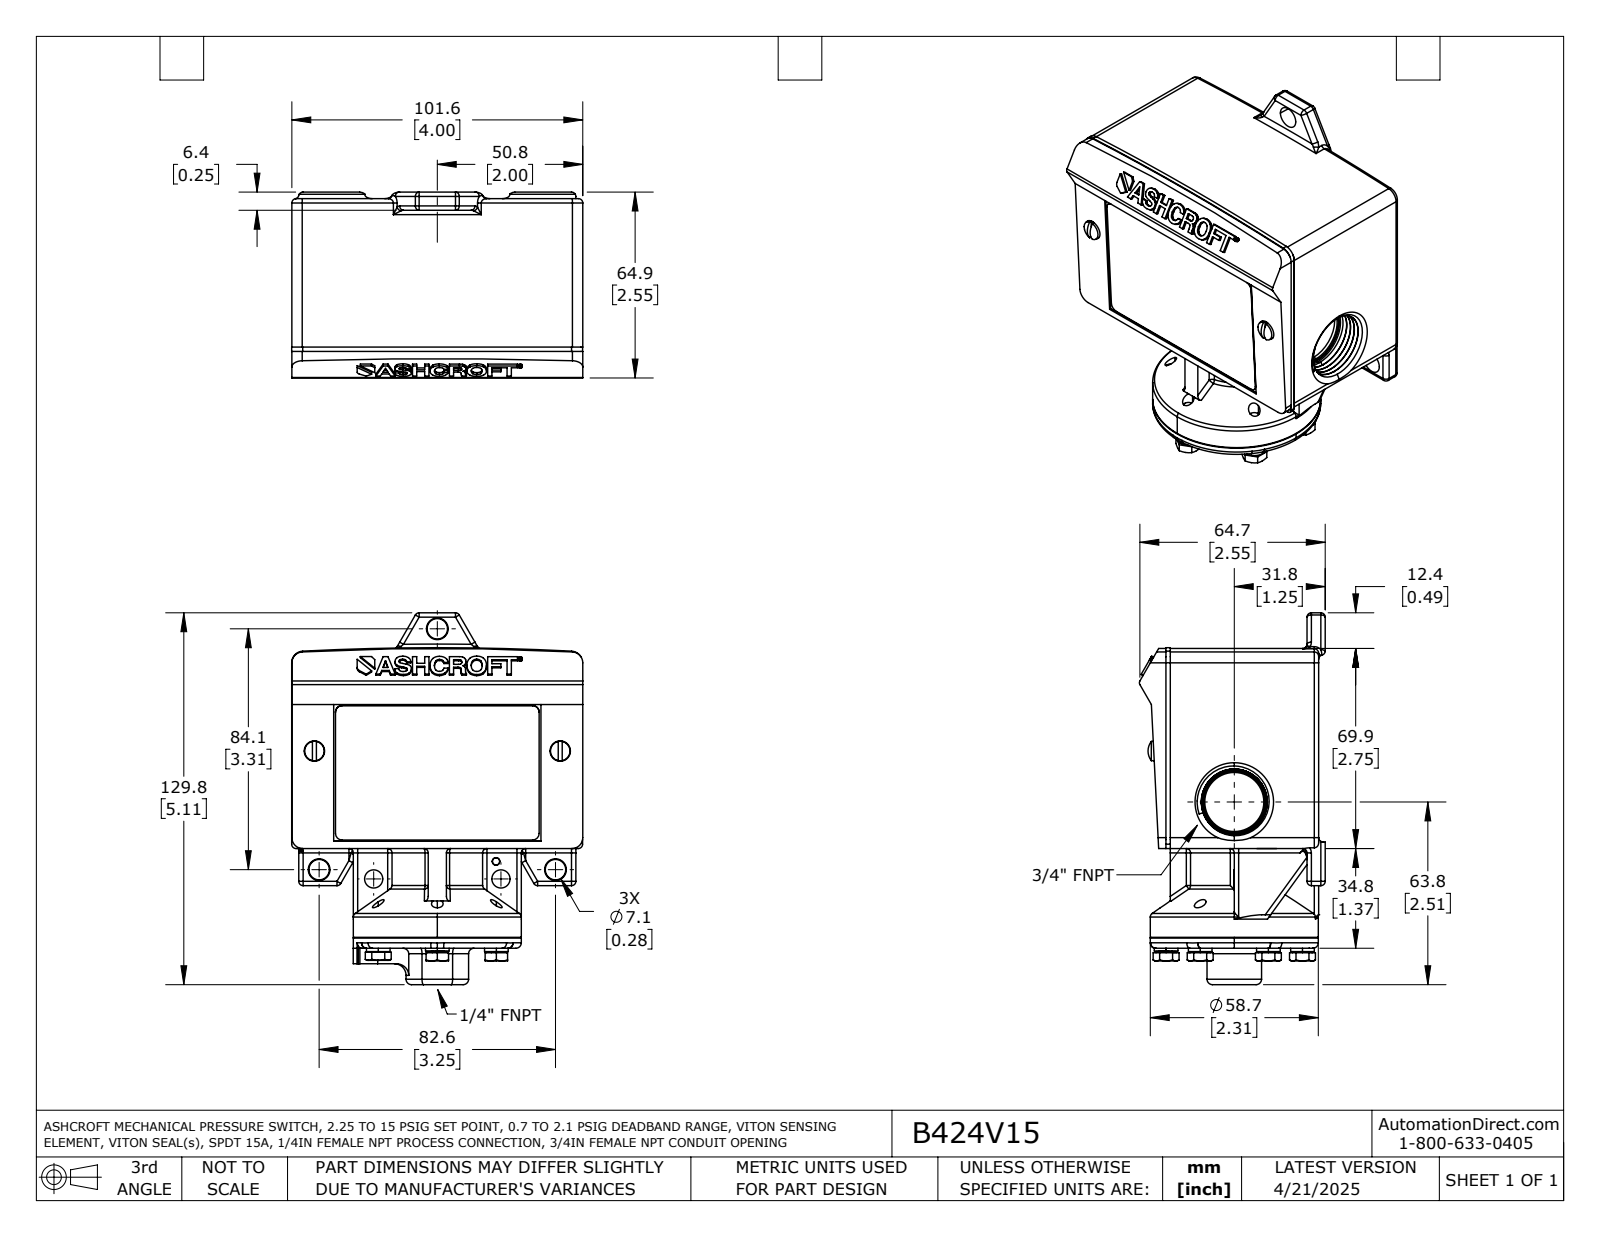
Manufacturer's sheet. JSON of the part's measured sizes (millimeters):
{"part_name": "B424V15", "step_written_by": "SolidWorks 2021 (AUTOMOTIVE_DESIGN)", "units": "millimeters", "bodies": {"solids": 2, "faces": 1259, "planar": 345, "cylindrical": 472, "other": 442}, "overall_size": [129.8, 101.7, 64.9], "volume_mm3": 468200, "surface_area_mm2": 54520, "round_holes": [[4.1, 6], [4.9, 5], [5.3, 5], [4.7, 4], [7.1, 2], [11.6, 1], [20.6, 1]], "round_bosses_or_shafts": [[8.3, 6], [7.1, 6], [4.8, 5], [6.9, 2], [6.4, 2], [58.7, 1]], "partial_cylinders_radius": [[1.5, 92], [0.8, 5], [1.9, 4], [2.3, 4], [3.8, 4], [0.3, 2], [2.4, 2], [4.1, 2]], "face_to_face_distances": [101.6, 0.4, 34.8, 2.3, 99.3, 11.2, 90.4, 88.1, 8.9, 21.5], "hole_center_spacings": [23.8, 41.2, 47.6, 23.8, 85.9]}
